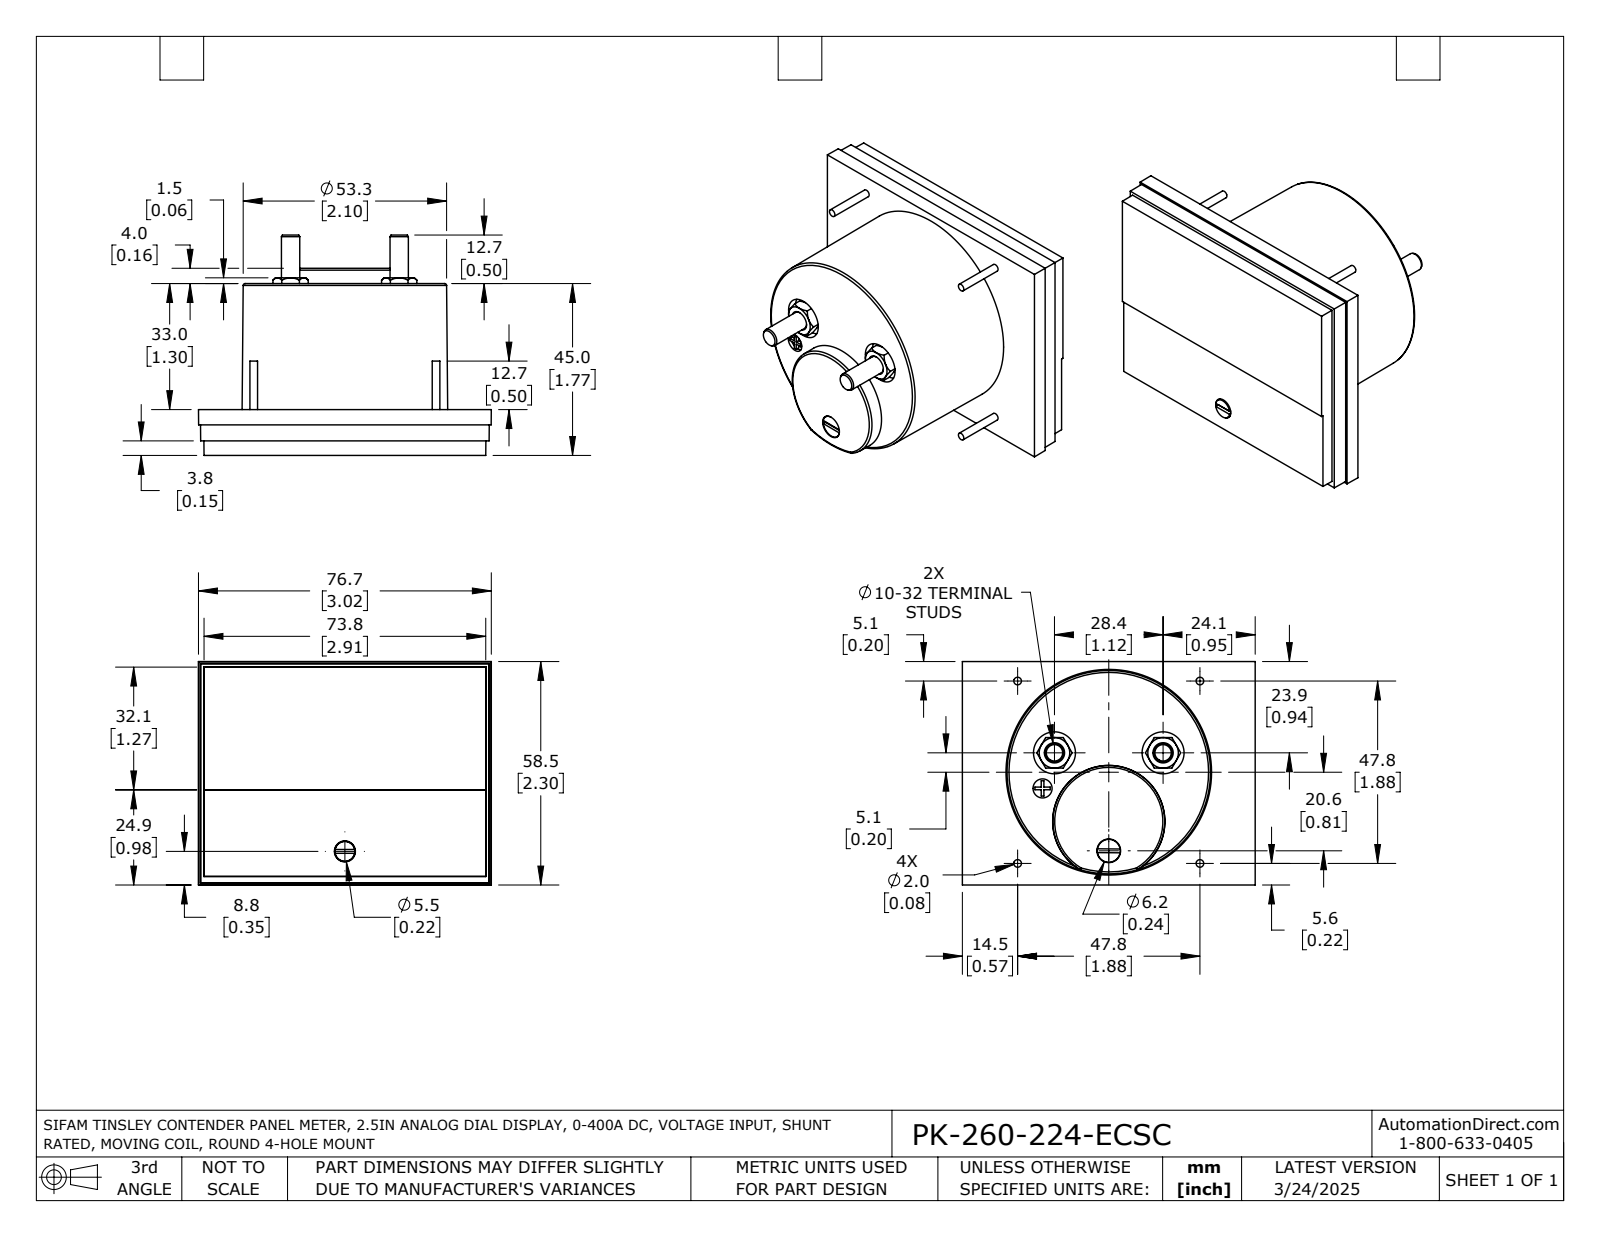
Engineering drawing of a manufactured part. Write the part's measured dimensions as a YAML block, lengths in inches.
part_name: "PK-260-224-ECSC"
step_written_by: "SolidWorks 2021 (AUTOMOTIVE_DESIGN)"
units: inches
bodies: {solids: 1, faces: 192, planar: 95, cylindrical: 37, other: 60}
overall_size: [3.02, 2.303, 2.272]
volume: 7.657
surface_area: 36.55
round_holes:
  - {diameter: 0.197, count: 3}
  - {diameter: 0.433, count: 2}
  - {diameter: 0.209, count: 1}
  - {diameter: 0.217, count: 1}
  - {diameter: 0.244, count: 1}
round_bosses_or_shafts:
  - {diameter: 0.079, count: 4}
  - {diameter: 0.189, count: 2}
  - {diameter: 0.236, count: 1}
  - {diameter: 0.205, count: 1}
partial_cylinders:
  - {radius: 0.033, count: 1}
face_to_face_distances: [0.02, 0.472, 0.13, 0.322, 0.15, 0.453, 0.057, 0.077, 0.396, 0.073]
hole_center_spacings: [1.155, 1.16, 0.387, 0.938, 0.942, 1.12, 1.295]
